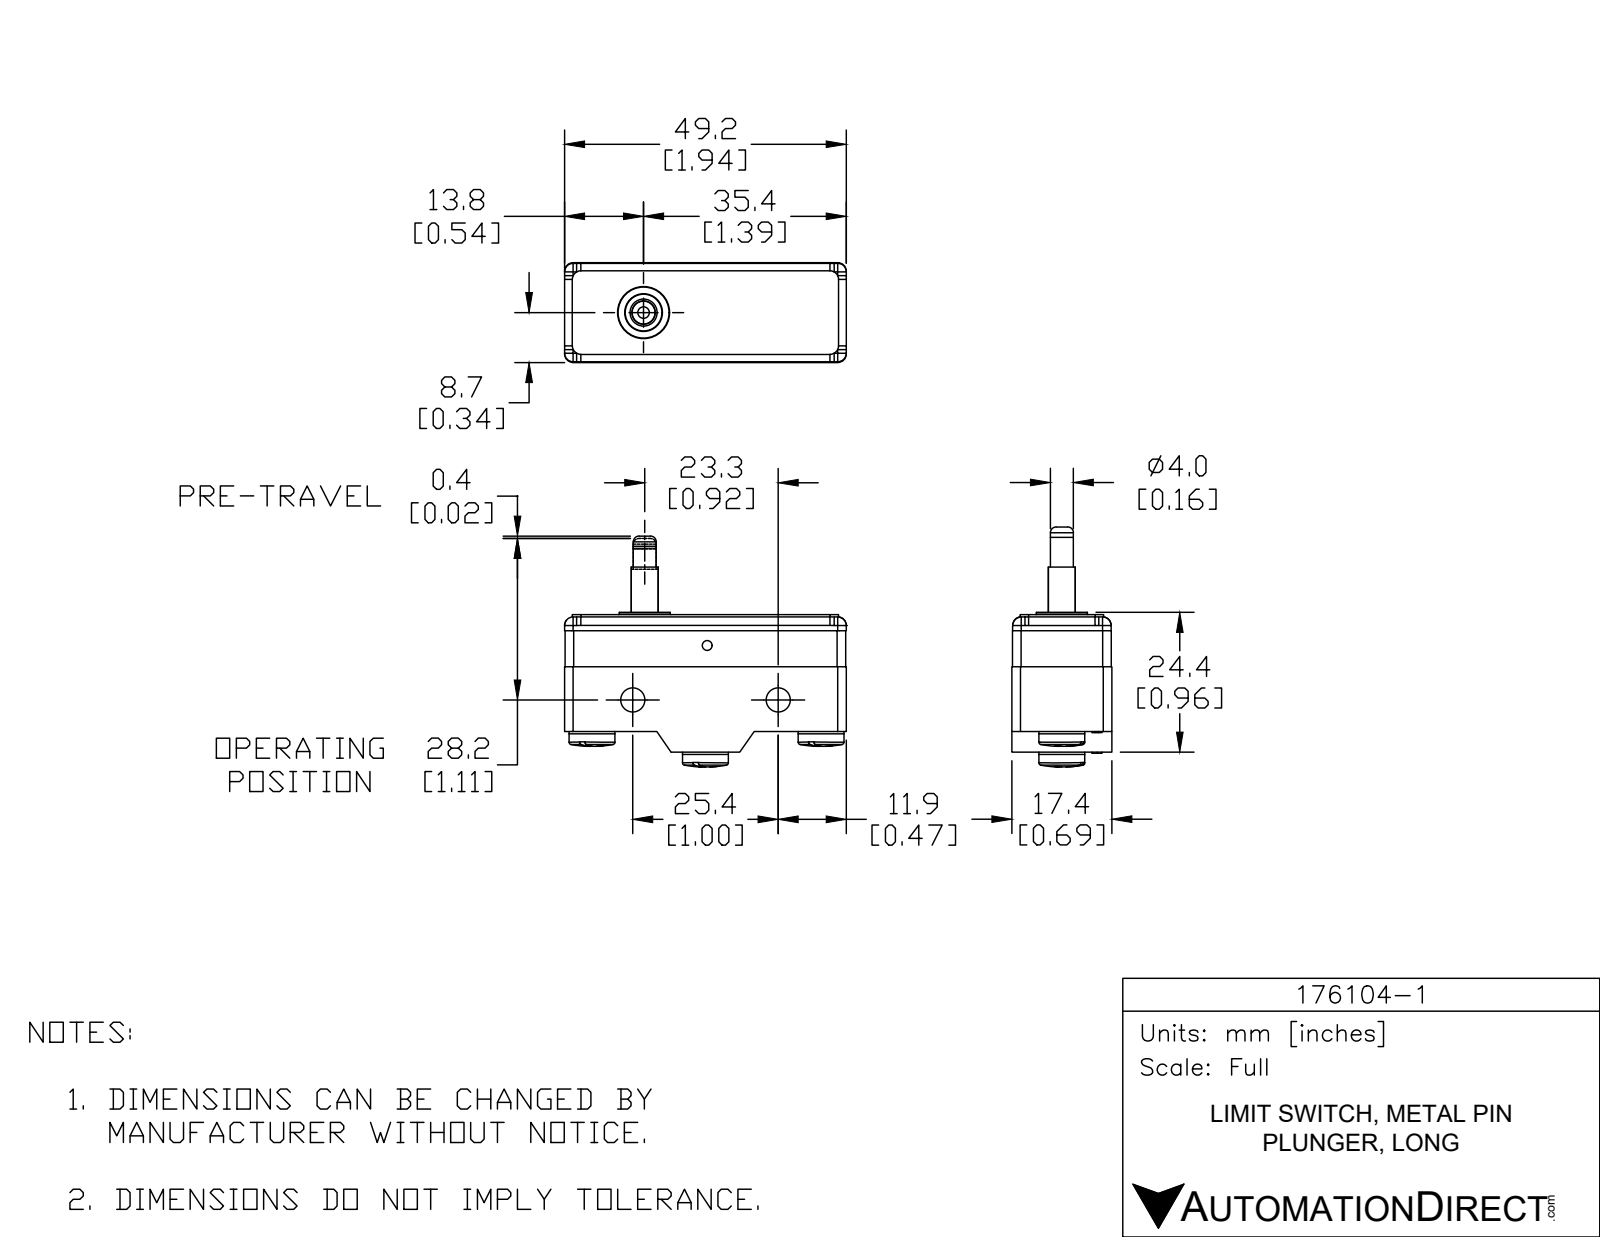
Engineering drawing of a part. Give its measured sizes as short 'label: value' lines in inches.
name: 176-MS (Screw Terminal)-Slim Spring Plunger
written by: SolidWorks 2018 (AUTOMOTIVE_DESIGN)
unit: in
bodies: 12 solids, 494 faces (204 planar, 126 cylindrical, 164 other)
size: 1.937 × 1.65 × 0.687
volume: 1.057 in³; area: 14.05 in²
holes: 3× ⌀0.15, 3× ⌀0.236, 2× ⌀0.165, 1× ⌀0.067, 1× ⌀0.161, 1× ⌀0.26
bosses: 3× ⌀0.315, 1× ⌀0.35, 1× ⌀0.252, 1× ⌀0.185, 1× ⌀0.157
rounds: 24× R0.059, 12× R0.012, 3× R0.116
face distances: 0.11, 0.683, 0.803, 0.693, 0.687, 0.142, 0.679, 0.016, 0.835, 0.945
hole spacings: 0.354, 0.425, 0.615, 0.634, 0.78, 0.795, 1, 1.22
